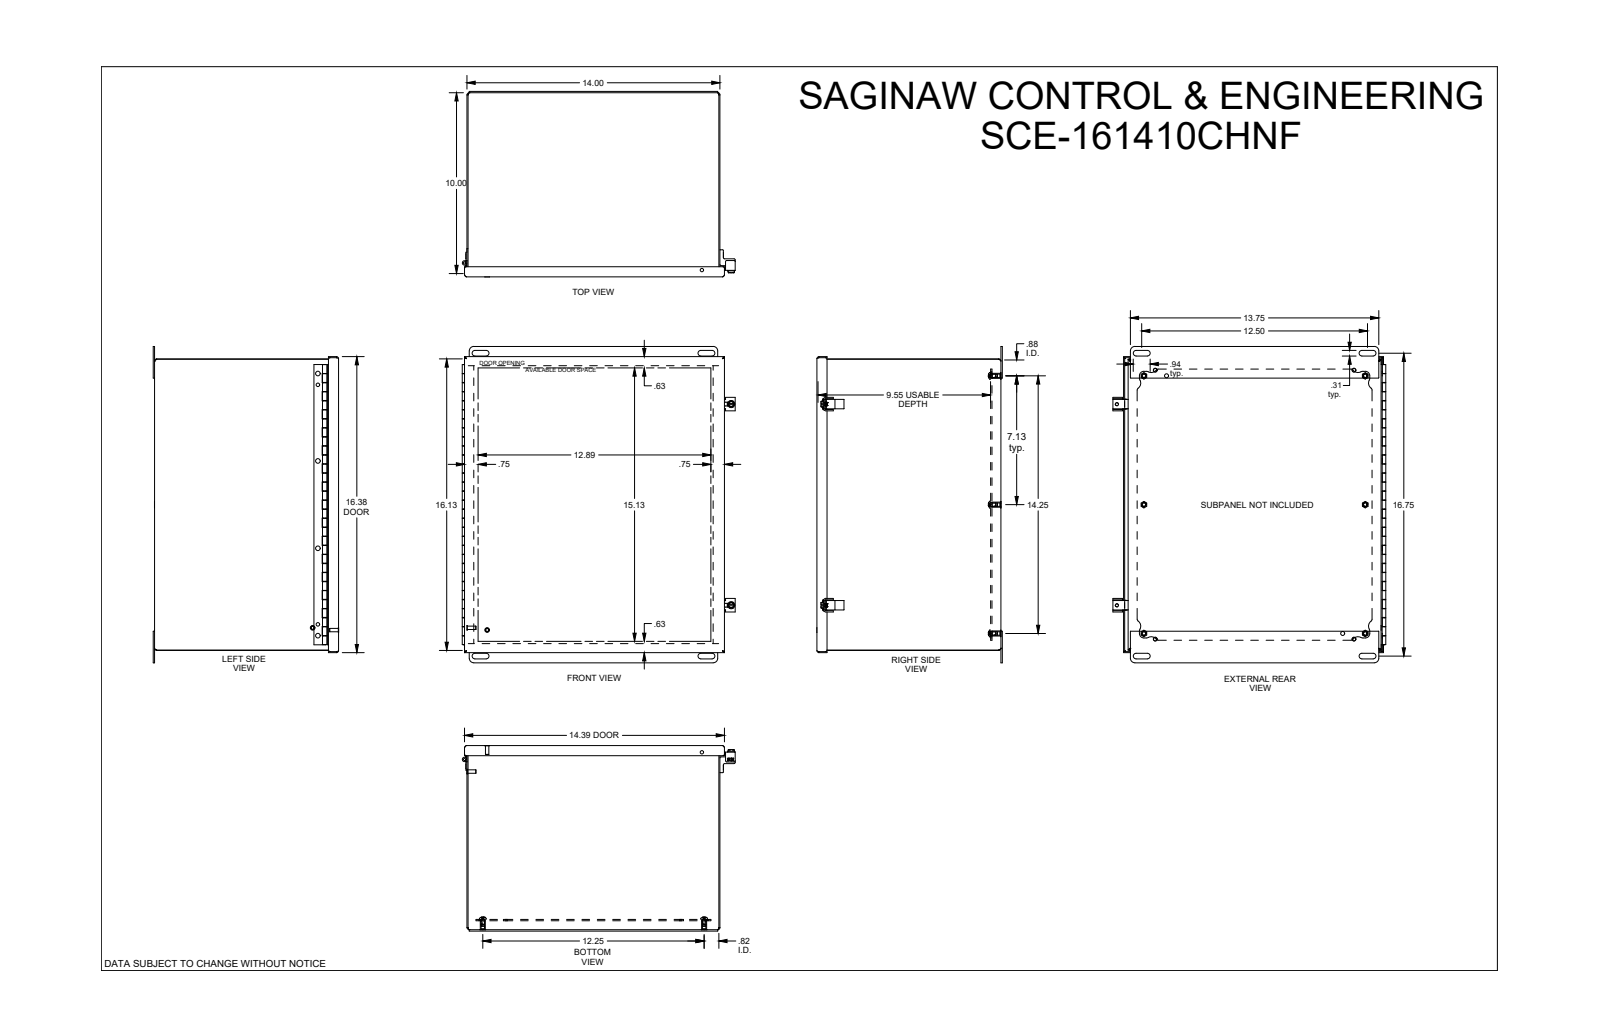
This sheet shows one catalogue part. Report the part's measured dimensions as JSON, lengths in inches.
{"part_name": "SCE-161410CHNF", "step_written_by": "SolidWorks 2019 (AUTOMOTIVE_DESIGN)", "units": "inches", "bodies": {"solids": 43, "faces": 1476, "planar": 656, "cylindrical": 391, "other": 429}, "overall_size": [17.5, 15.104, 10.265], "volume_in3": 90.53, "surface_area_in2": 2856, "round_holes": [[0.19, 12], [0.193, 8], [0.25, 6], [0.203, 4], [0.281, 4], [0.156, 2], [0.218, 2], [0.266, 2], [0.126, 1], [0.187, 1]], "round_bosses_or_shafts": [[0.188, 14], [0.256, 8], [0.373, 6], [0.28, 6], [0.396, 2], [0.188, 2], [0.246, 1], [0.123, 1]], "partial_cylinders_radius": [[0.01, 82], [0.06, 33], [0.25, 16], [0.05, 8], [0.125, 8], [0.156, 8], [0.344, 8], [0.027, 6]], "face_to_face_distances": [0.06, 10.125, 13.94, 16.065, 10.185, 10.065, 0.075, 0.51, 0.435, 0.57], "hole_center_spacings": [14.172, 0.699, 18.792, 0.7, 7.464, 11.63, 11.63, 12.251]}
